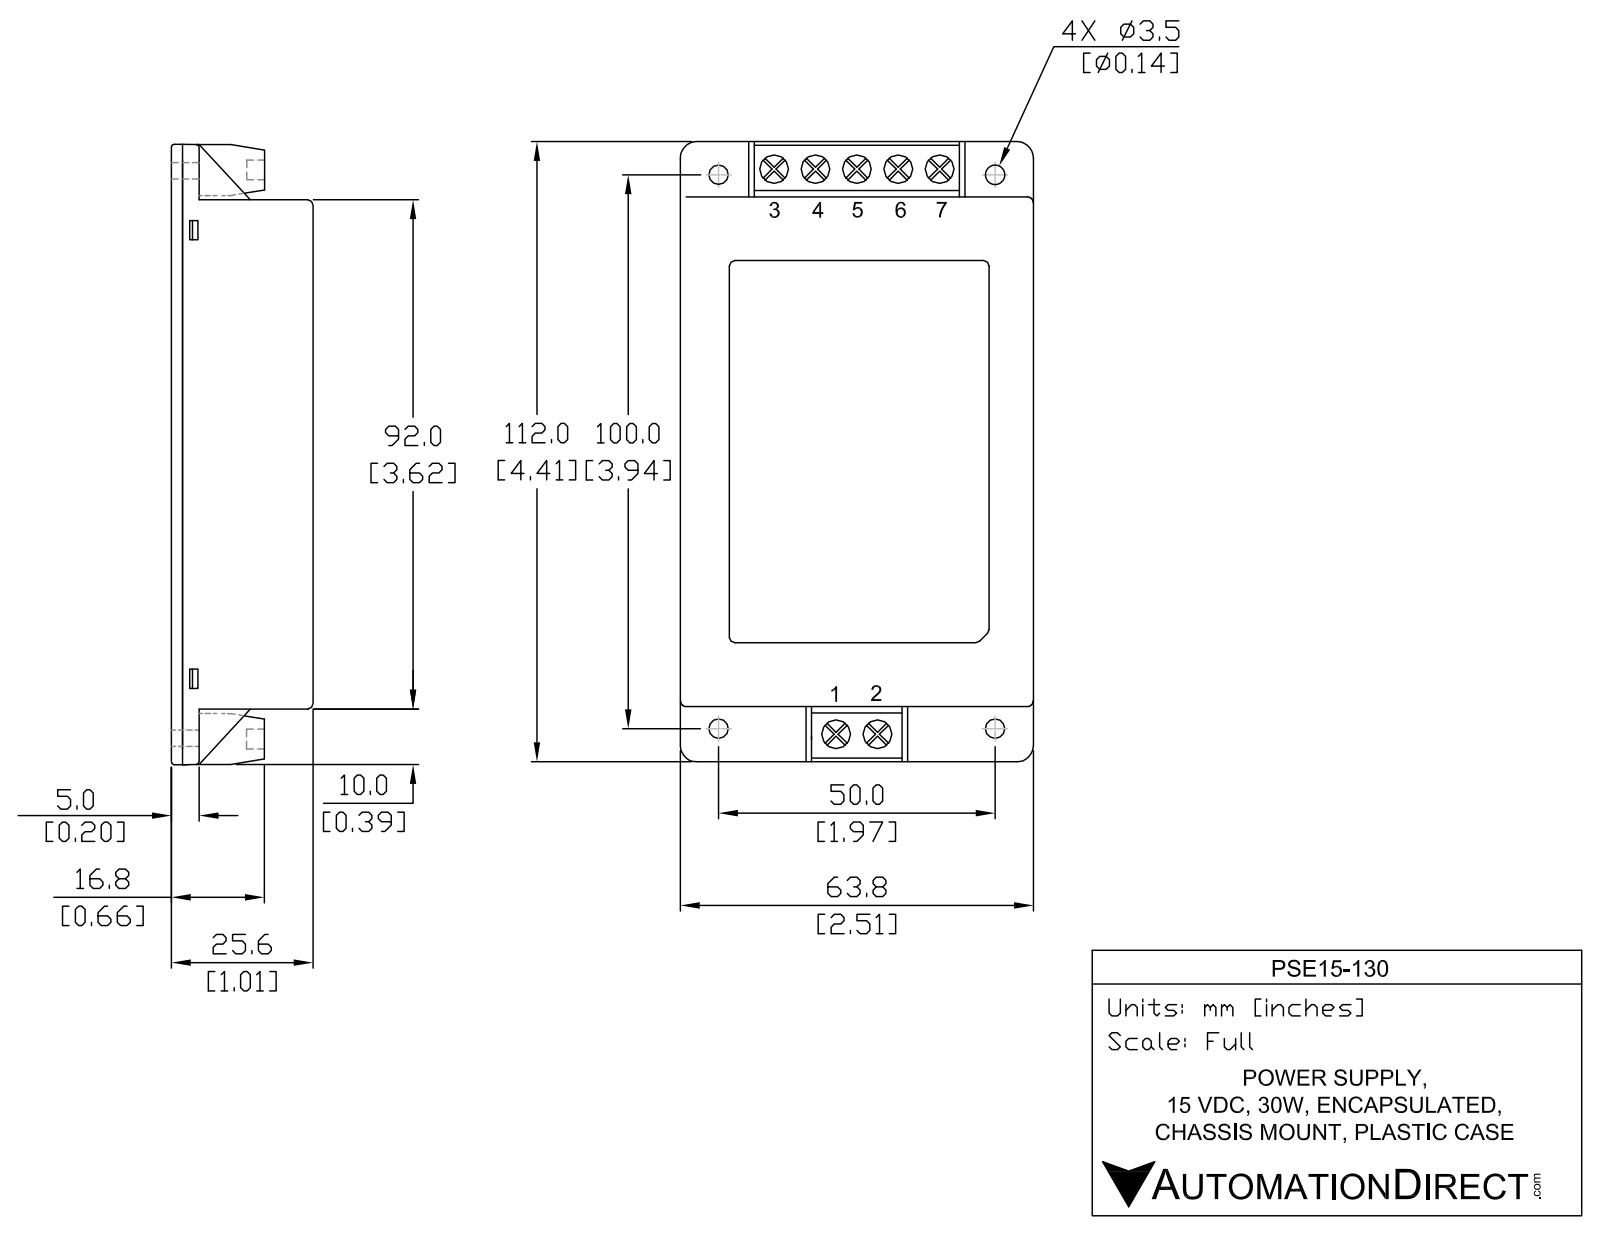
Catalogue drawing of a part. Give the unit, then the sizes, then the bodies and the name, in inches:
Units: inches
Overall size (bounding box): 4.41 × 2.51 × 1.01
Round holes (diameter × count): ⌀0.2 ×7, ⌀0.14 ×4
Partial cylindrical surfaces — rounded edges, fillets, slot ends (radius × count): R0.03 ×20, R0.125 ×4
Main face-to-face distances: 0.078, 0.08, 0.93, 1.008, 0.928, 1.01, 0.932, 2.51, 3.62, 0.015
Hole centre spacings: 0.26, 0.52, 0.26, 0.856, 1.116, 1.97, 3.94, 4.015
Volume: 9.834 in³ · Surface area: 60.49 in²
Bodies: 2 solids, 374 faces (246 planar, 62 cylindrical, 66 other)
Part name (STEP PRODUCT): PSE15-130
STEP written by: SolidWorks 2011 (CONFIG_CONTROL_DESIGN)
